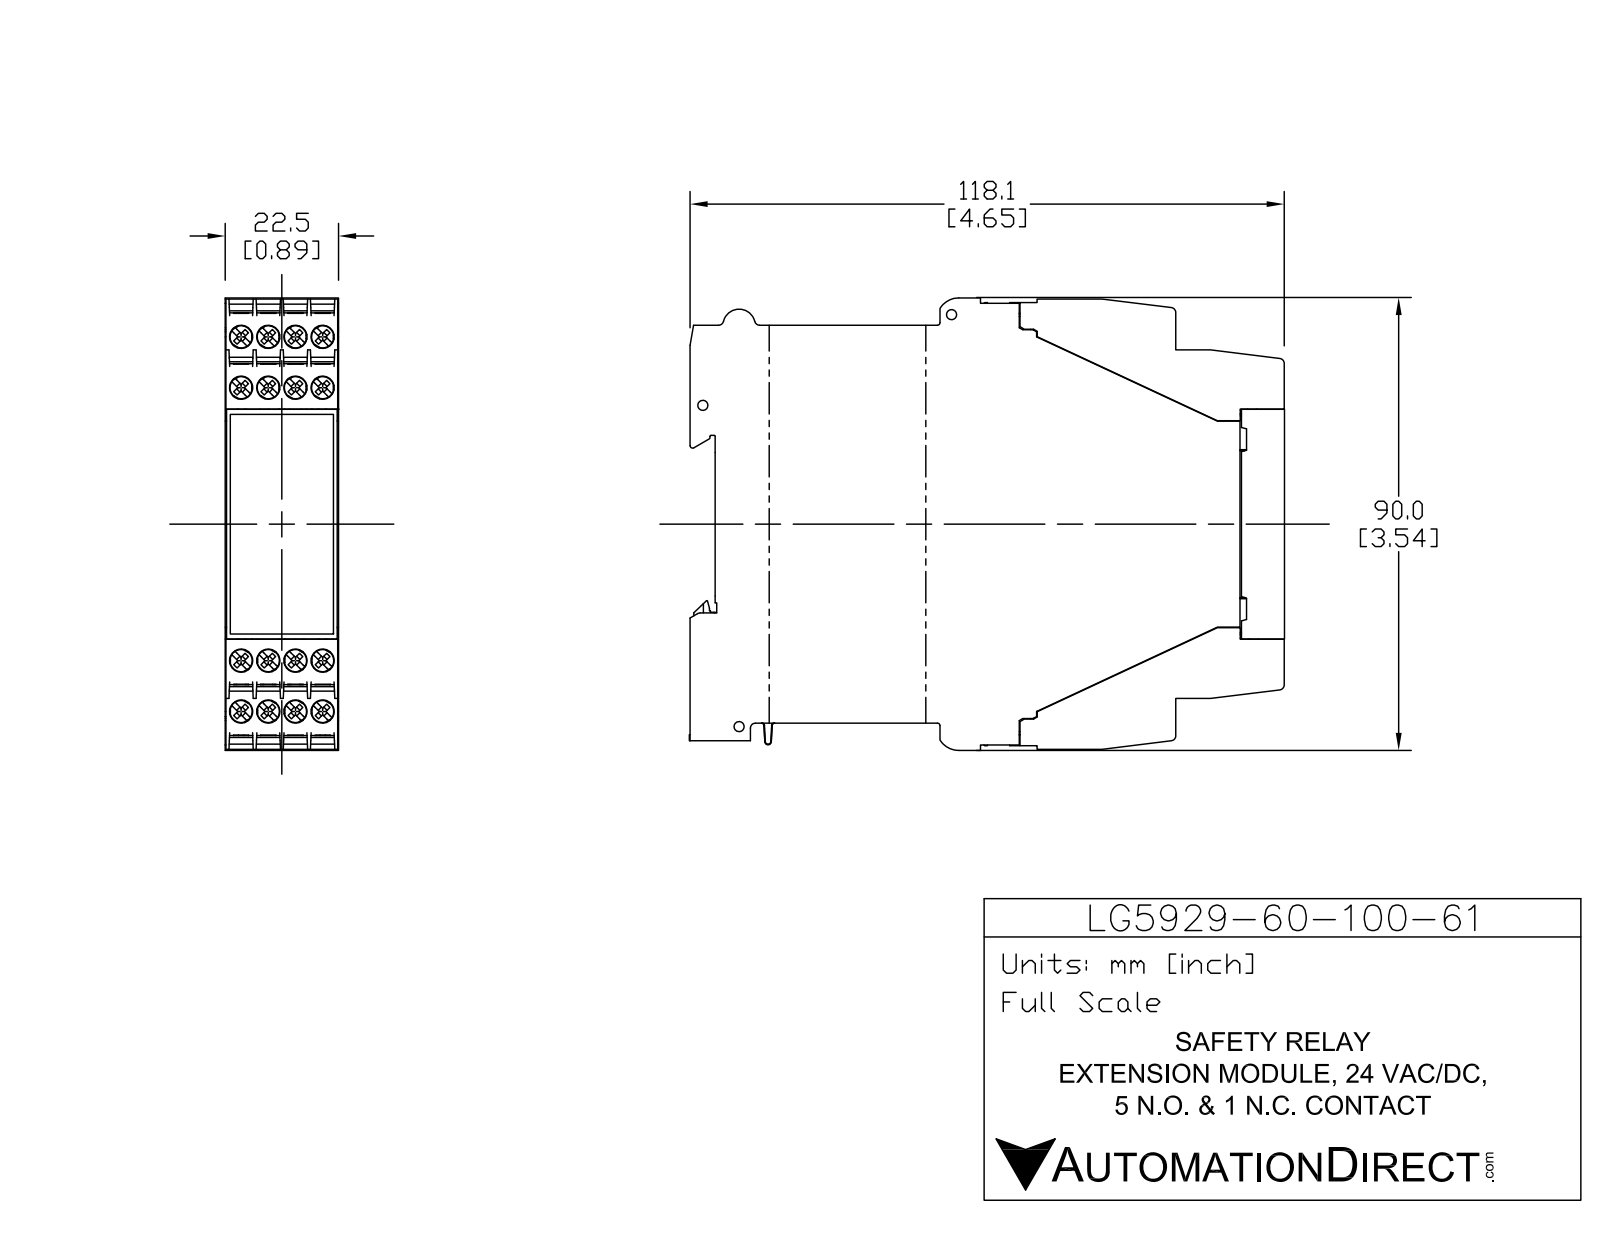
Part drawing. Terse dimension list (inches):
name: LG5929-60-100-61
written by: SolidWorks 2017 (AUTOMOTIVE_DESIGN)
unit: in
bodies: 18 solids, 940 faces (815 planar, 83 cylindrical, 42 other)
size: 4.646 × 4.01 × 0.906
volume: 14.56 in³; area: 73.74 in²
holes: 4× ⌀0.039, 4× ⌀0.067, 1× ⌀0.049
bosses: 1× ⌀0.053
rounds: 10× R0.004, 8× R0.039, 7× R0.02, 6× R0.005, 4× R0.004, 3× R0.008, 3× R0.021, 2× R0.012
face distances: 0.906, 0.896, 0.398, 0.9, 0.89, 2.346, 0.183, 2.927, 0.848, 0.581
hole spacings: 0.638, 0.848, 1.061
